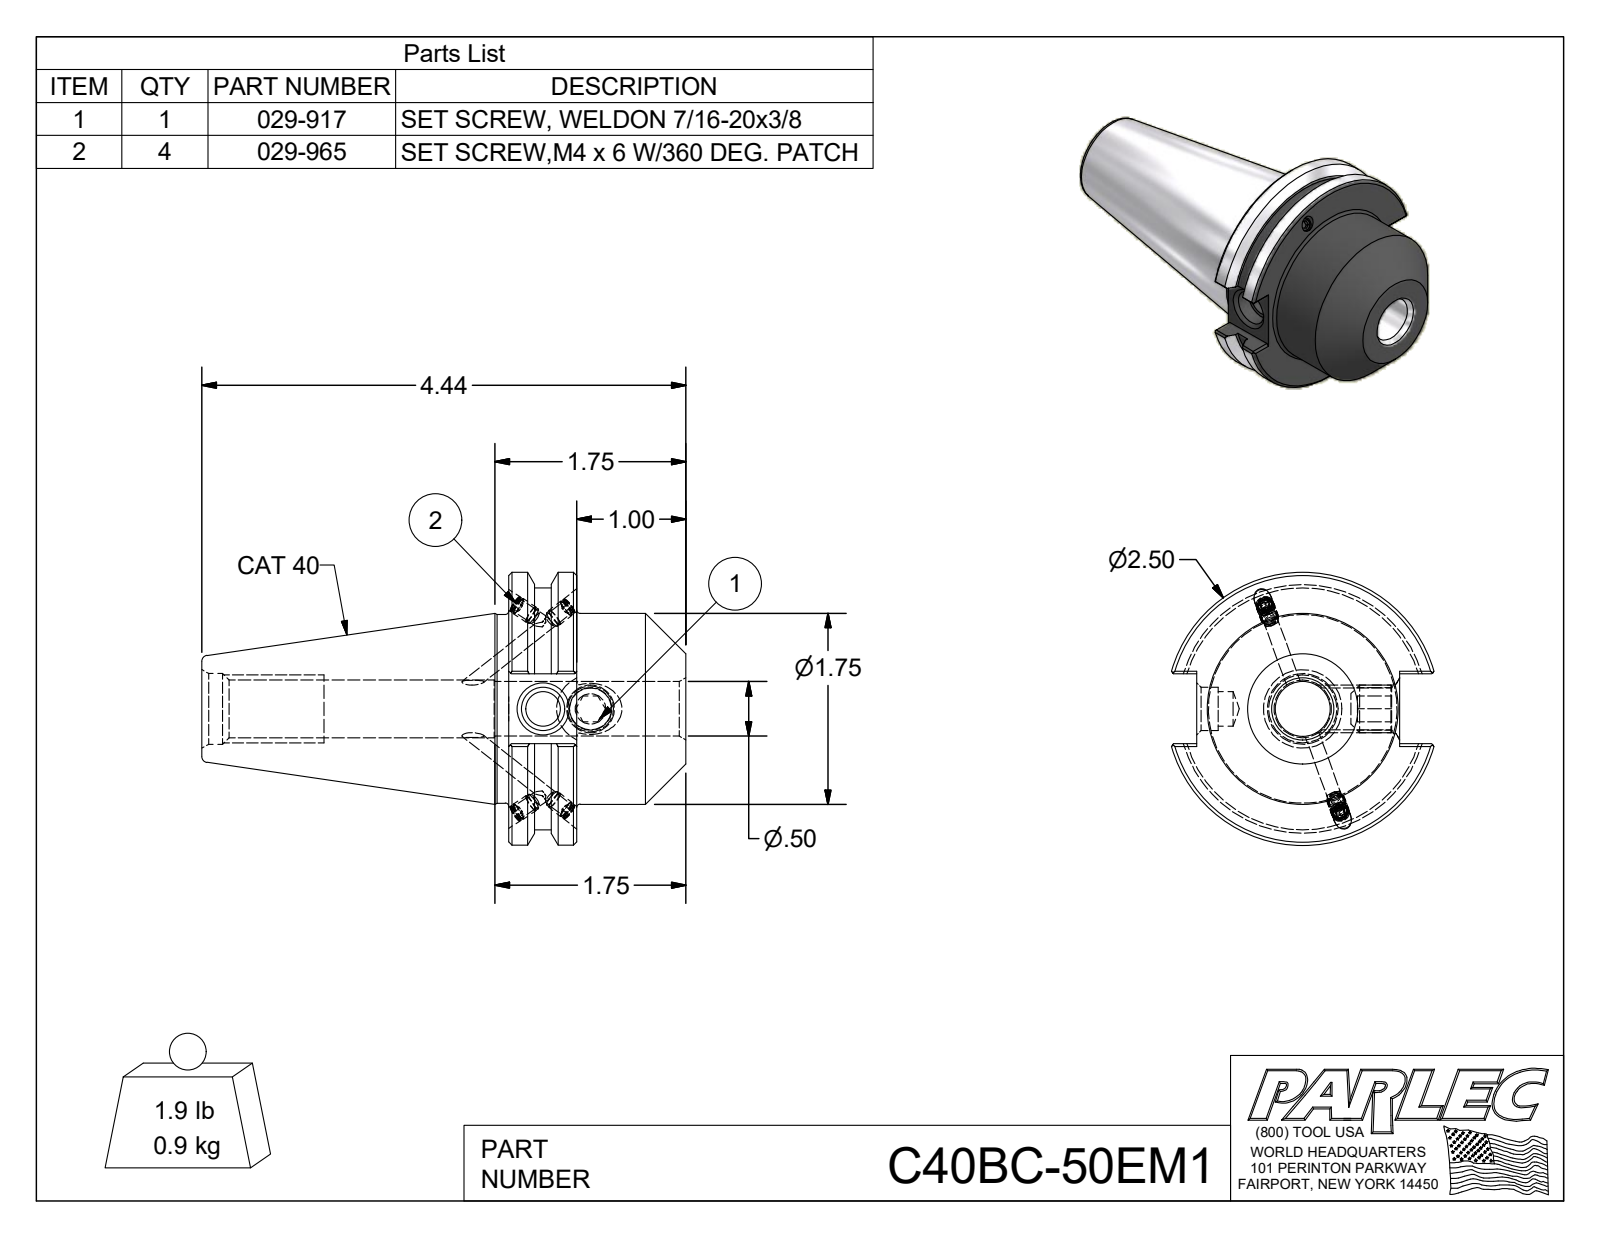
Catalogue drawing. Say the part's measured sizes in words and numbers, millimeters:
The part is named "C40BC-50EM1; C40BC-50EM1-1; 029-917; 029-965". Its 3-D file was written by "Autodesk Inventor 2012 (AUTOMOTIVE_DESIGN)". It is 6 solids with 158 faces: 84 planar, 35 cylindrical and 39 other. Overall it measures 112.7 by 63.5 by 61 millimeters. Its volume is 130 400 cubic millimeters and its surface area 25 970 square millimeters. Round holes: 4 of diameter 3.3, 4 of diameter 4.1, 1 of diameter 8, 1 of diameter 9.7, 1 of diameter 10.1, 1 of diameter 12.7, 1 of diameter 13.4, 1 of diameter 16.5. Round bosses or shafts: 4 of diameter 4.2, 4 of diameter 4, 1 of diameter 63.5, 1 of diameter 56.4, 1 of diameter 44.5, 1 of diameter 43.9, 1 of diameter 11.1. The main face-to-face distances are 15.9, 41.3, 25.4, 6, 16.3, 47.2, 71.5, 87.3, 112.7, 81.3. The hole center spacings are 11.
